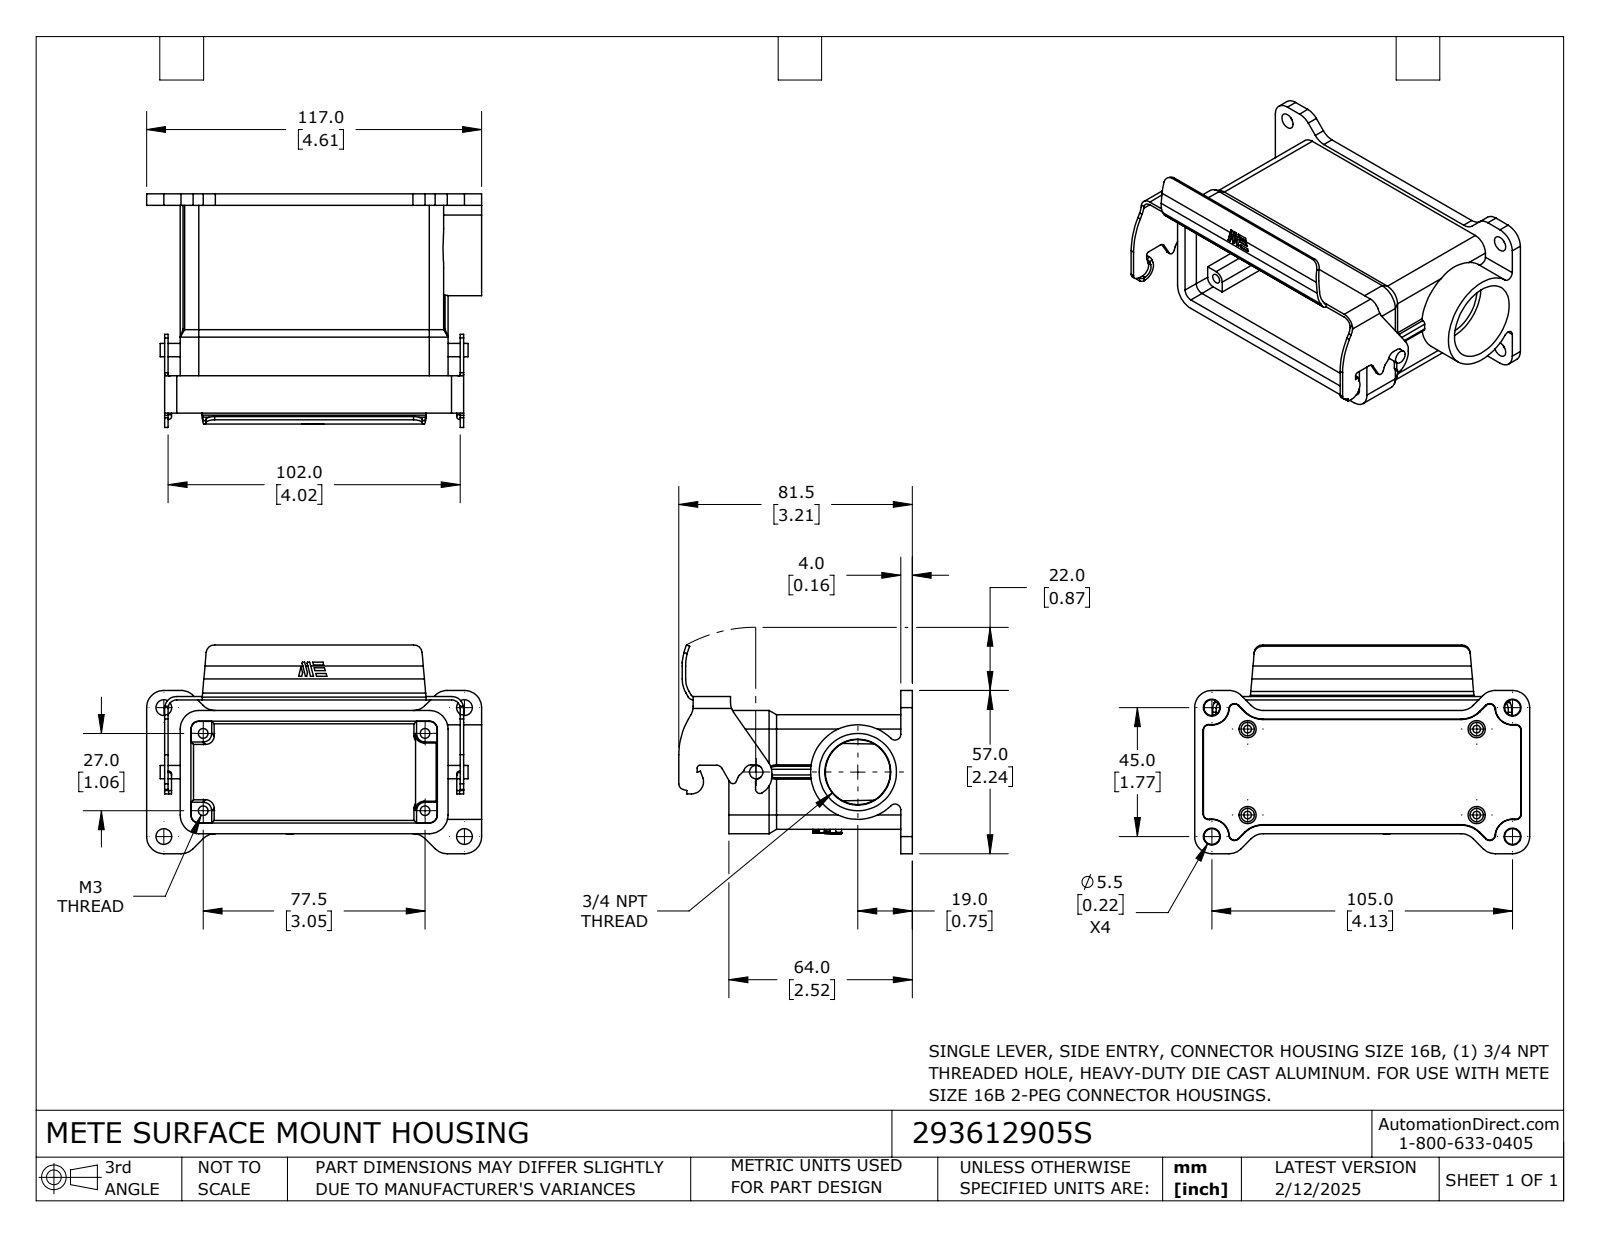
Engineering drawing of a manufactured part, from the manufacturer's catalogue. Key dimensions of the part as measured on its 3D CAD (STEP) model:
Part name (STEP PRODUCT): 293612905S
STEP written by: SolidWorks 2024 (CONFIG_CONTROL_DESIGN)
Units: inches
Bodies: 1 solid, 397 faces (195 planar, 148 cylindrical, 54 other)
Overall size (bounding box): 4.606 × 3.209 × 2.87
Volume: 4.683 in³ · Surface area: 84.93 in²
Round holes (diameter × count): ⌀0.134 ×4, ⌀1.063 ×1
Round bosses / shafts (diameter × count): ⌀0.185 ×1
Partial cylindrical surfaces — rounded edges, fillets, slot ends (radius × count): R0.008 ×26, R0.236 ×14, R0.039 ×10, R0.02 ×9, R0.118 ×9, R0.079 ×5, R0.11 ×4, R0.197 ×4
Main face-to-face distances: 0.059, 0.098, 1.575, 0.047, 1.634, 0.146, 1.693, 0.284, 0.157, 0.205
Hole centre spacings: 1.063, 3.051, 3.231
